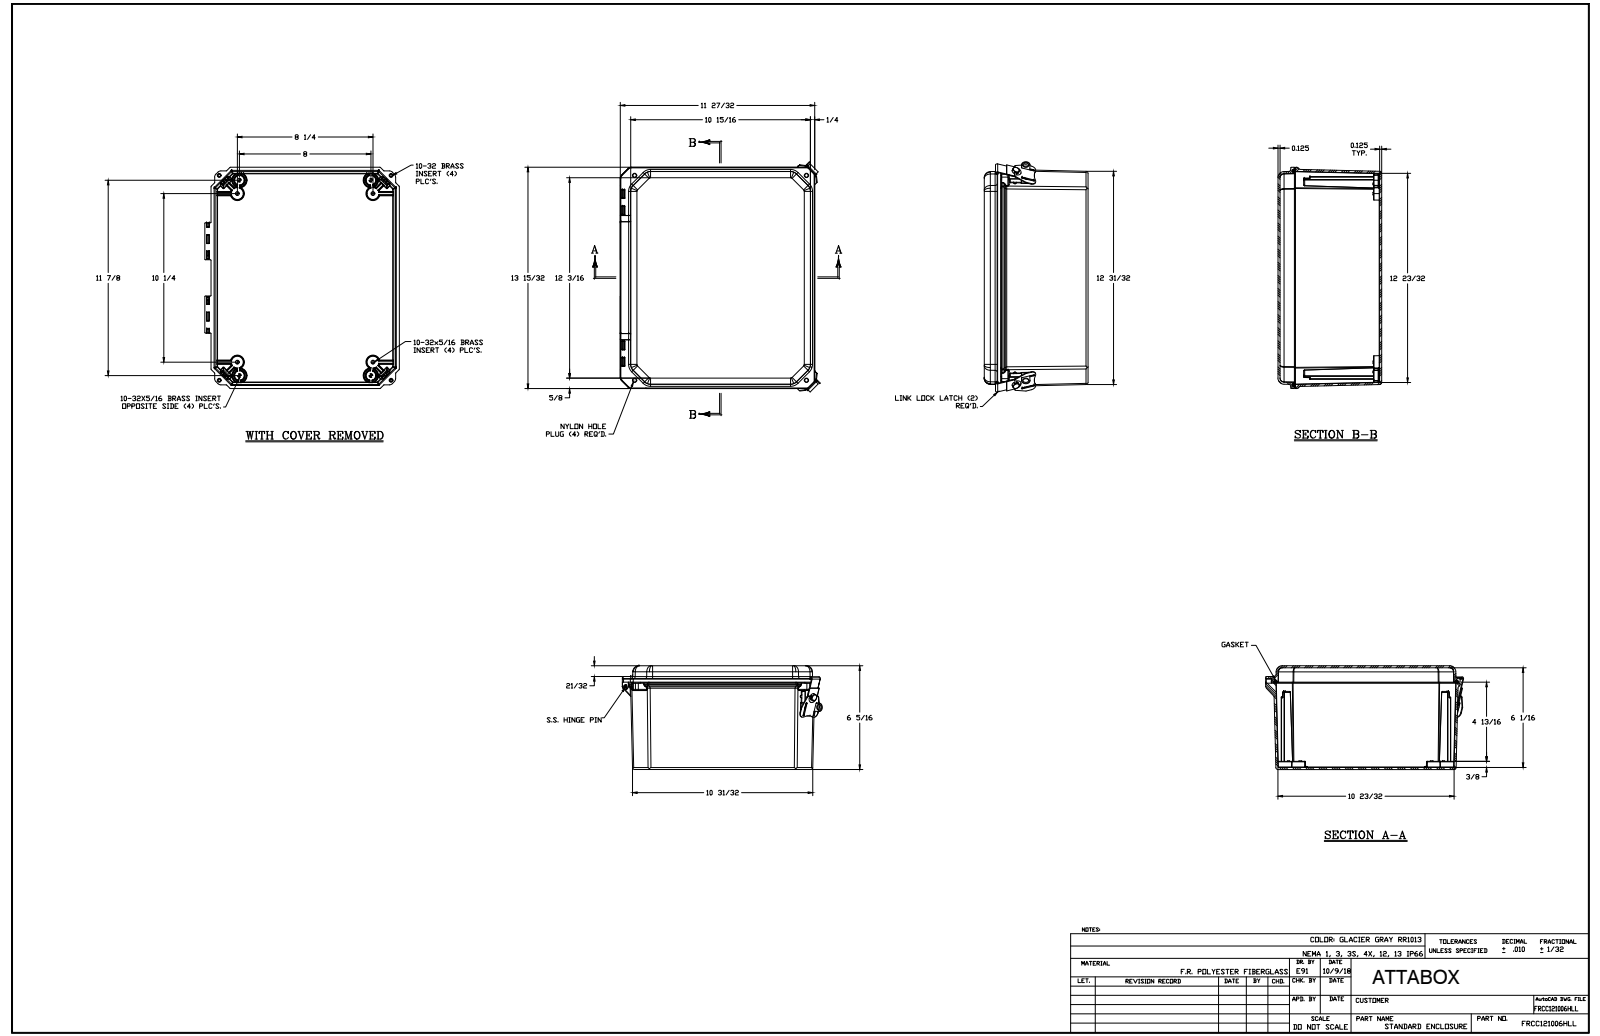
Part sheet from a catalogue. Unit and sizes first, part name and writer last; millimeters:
Units: millimetres
Overall size (bounding box): 364.1 × 311.7 × 160.3
Round holes (diameter × count): ⌀4 ×12, ⌀3.9 ×8, ⌀3.8 ×4, ⌀5.6 ×4, ⌀6.4 ×4, ⌀7.9 ×4, ⌀1.3 ×2, ⌀2.5 ×2, ⌀3 ×2, ⌀9.2 ×2, ⌀3.5 ×1
Round bosses / shafts (diameter × count): ⌀6.2 ×12, ⌀22.1 ×4, ⌀5.3 ×4, ⌀1.3 ×4, ⌀3.4 ×3, ⌀15.2 ×2, ⌀5.1 ×2
Partial cylindrical surfaces — rounded edges, fillets, slot ends (radius × count): R0.3 ×208, R0.1 ×94, R0.5 ×59, R3.2 ×41, R0.8 ×37, R1 ×28, R6.4 ×26, R0.8 ×24
Main face-to-face distances: 3.2, 157.1, 154, 160.3, 3.5, 3.6, 3.6, 140.5, 16.7, 25.4
Hole centre spacings: 289.7, 373.6, 387.8, 20.9, 32, 39.6, 207.4, 234.5
Volume: 1 379 000 mm³ · Surface area: 820 600 mm²
Bodies: 33 solids, 2265 faces (661 planar, 890 cylindrical, 714 other)
Part name (STEP PRODUCT): FRCC121006HLL
STEP written by: SolidWorks 2018 (AUTOMOTIVE_DESIGN)
